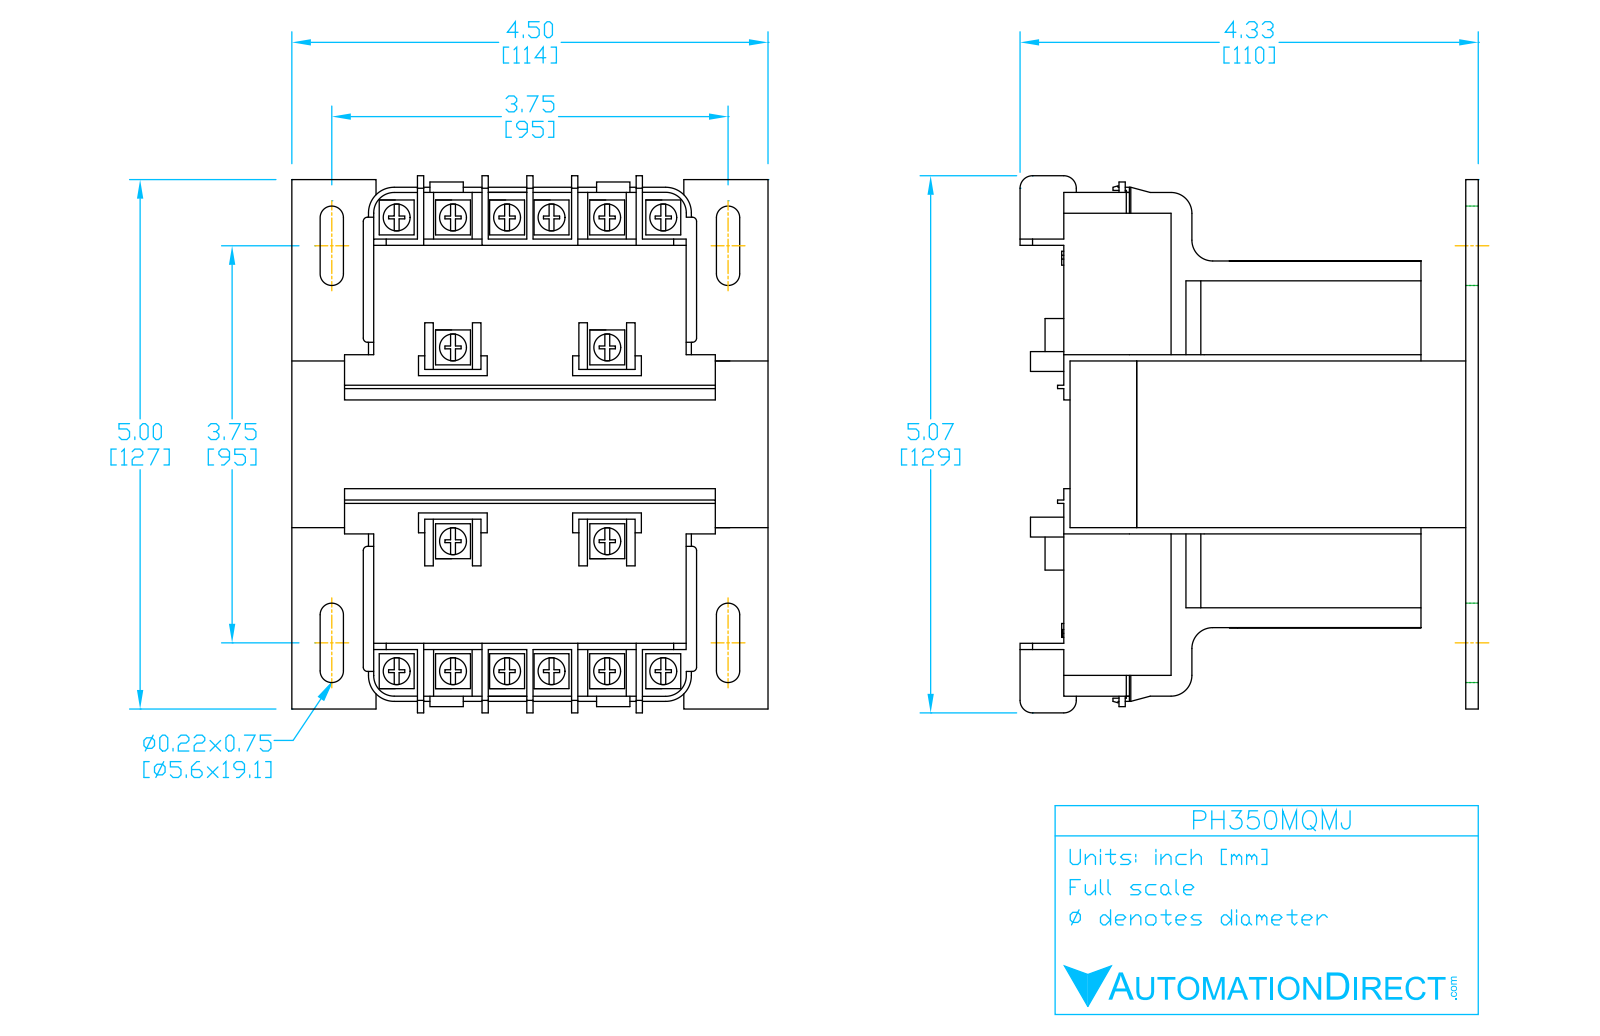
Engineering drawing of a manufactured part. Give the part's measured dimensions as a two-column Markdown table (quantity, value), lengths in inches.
| quantity | value |
| --- | --- |
| part name | PH350MQMJ |
| STEP written by | SolidWorks 2017 (AUTOMOTIVE_DESIGN) |
| units | inches |
| bodies | 8 solids, 612 faces (340 planar, 194 cylindrical, 78 other) |
| overall size | 5.075 × 4.5 × 4.331 |
| volume | 62.24 in³ |
| surface area | 215 in² |
| round holes (diameter × count) | 0.157 × 8 |
| partial cylindrical surfaces (radius × count) | 0.039 × 90, 0.197 × 18, 0.11 × 8, 0.118 × 4, 0.243 × 4 |
| main face-to-face distances | 1.575, 3.858, 0.187, 2.992, 3.179, 4.213, 1.22, 1.033, 0.63, 3.74 |
| hole center spacings | 3.75, 3.991, 0.383, 1.367, 3.769, 0.984, 3.877, 4.138 |
